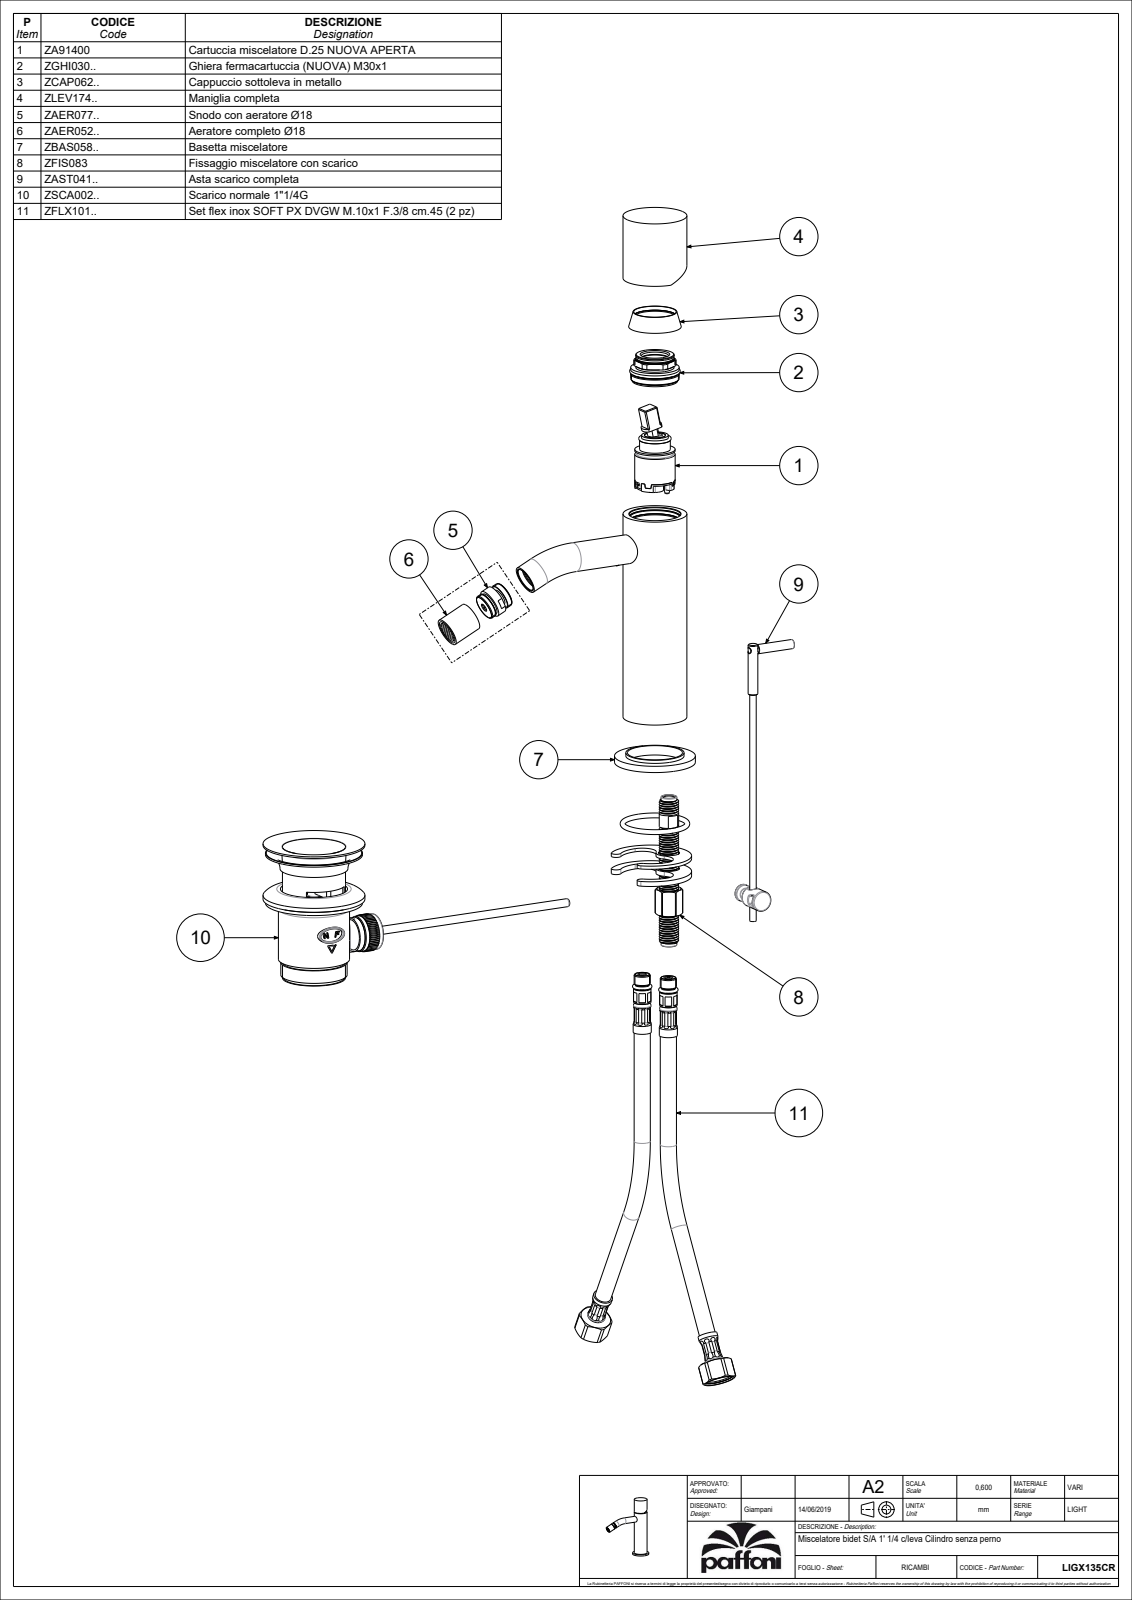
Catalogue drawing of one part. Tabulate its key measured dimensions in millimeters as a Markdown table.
| quantity | value |
| --- | --- |
| part name | LIGX135CR |
| STEP written by | CREO PARAMETRIC BY PTC INC, 2020044 (CONFIG_CONTROL_DESIGN) |
| units | millimeters |
| bodies | 0 solids, 58 faces (16 planar, 24 cylindrical, 18 other) |
| overall size | 175.89 × 165.4 × 50 |
| round bosses / shafts (diameter × count) | 18 × 4, 50 × 1, 39.5 × 1, 10 × 1, 7.6 × 1, 5.7 × 1 |
| partial cylindrical surfaces (radius × count) | 0.8 × 2, 3 × 2 |
| main face-to-face distances | 4, 134, 130, 2.5, 5.5, 18.49, 26.49, 8, 23.99, 135.04 |
